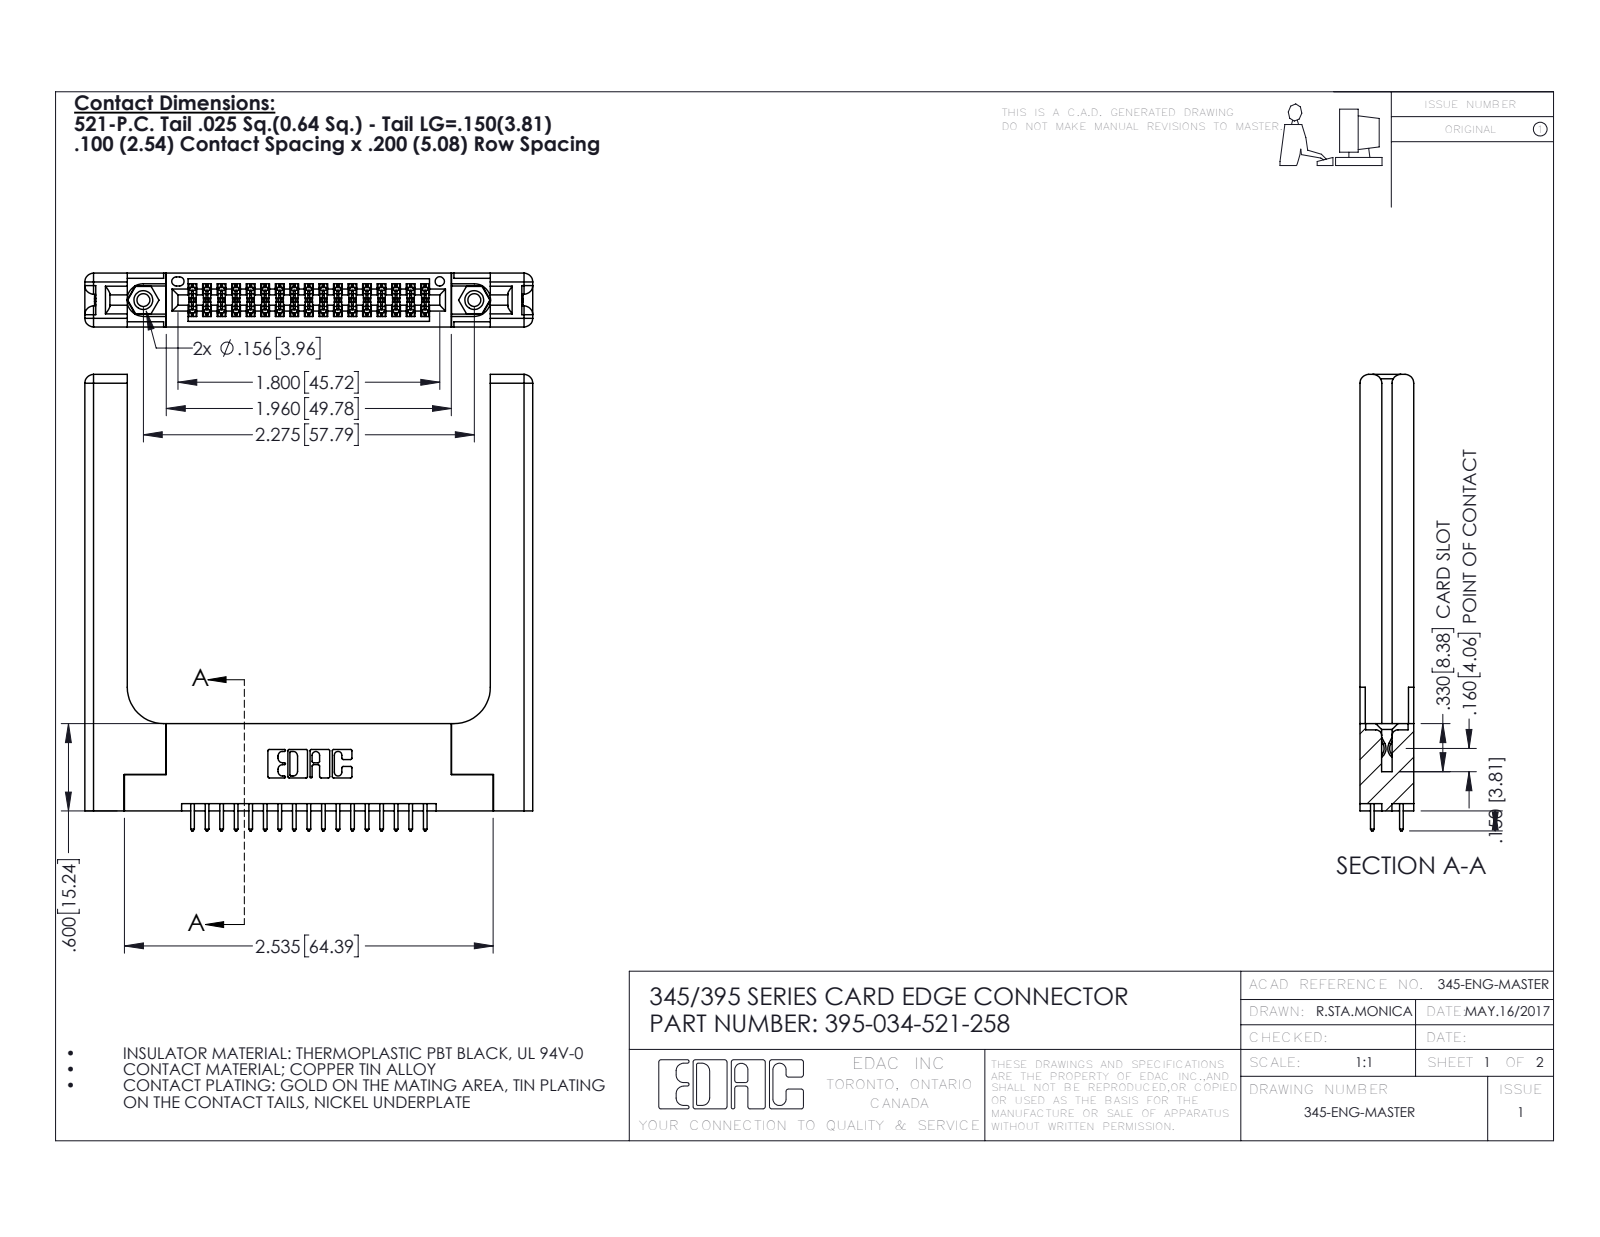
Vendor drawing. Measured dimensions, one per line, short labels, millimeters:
name: 345 Part_Flush Mounting Lugs - 0.156 Dia-TH; 345-250-001_345-250-001-102; 395-034-521-258; 345-220-058_345-220-058 (+1 more)
written by: SolidWorks 2016 (CONFIG_CONTROL_DESIGN)
unit: mm
bodies: 39 solids, 2082 faces (1350 planar, 672 cylindrical, 60 other)
size: 79.7 × 78.2 × 9.4
volume: 15 800 mm³; area: 15 350 mm²
holes: 2× ⌀2.3, 2× ⌀3.2, 2× ⌀4, 1× ⌀1.6
bosses: 2× ⌀3.9
rounds: 51× R0.2, 34× R0.3, 22× R0.3, 16× R1.5, 6× R0.2, 6× R0.8, 3× R0.7, 2× R0.4
face distances: 9.4, 1.8, 7.6, 5.1, 3.8, 3.8, 2, 5.6, 5.7, 2.5
hole spacings: 6.9, 51.8, 57.8
